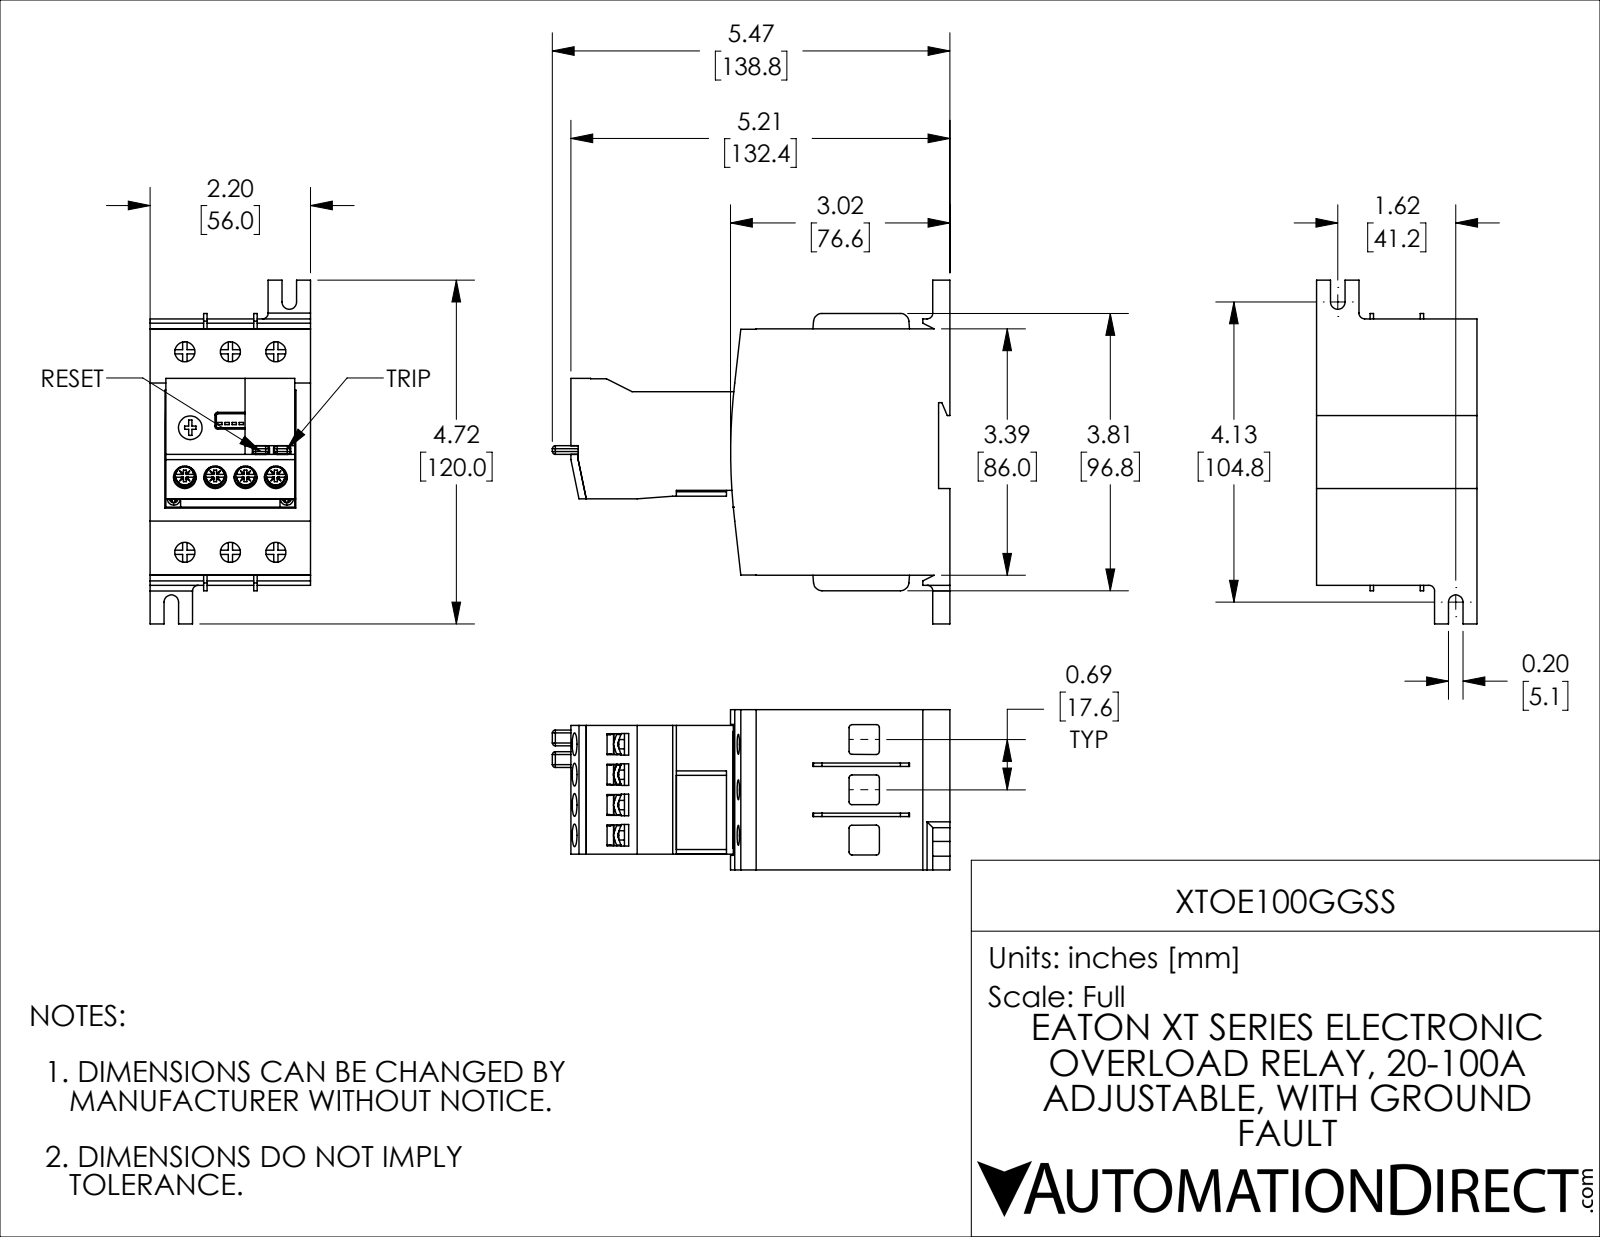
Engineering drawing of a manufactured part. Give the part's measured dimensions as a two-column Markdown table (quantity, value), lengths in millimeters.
| quantity | value |
| --- | --- |
| part name | XTOE100GGSS |
| STEP written by | SolidWorks 2018 (AUTOMOTIVE_DESIGN) |
| units | millimeters |
| bodies | 31 solids, 1045 faces (690 planar, 189 cylindrical, 166 other) |
| overall size | 138.9 × 120 × 56 |
| volume | 447 700 mm³ |
| surface area | 60 500 mm² |
| round holes (diameter × count) | 7 × 6, 3.6 × 4, 6.8 × 4, 8 × 4, 2.2 × 2, 3.2 × 2 |
| round bosses / shafts (diameter × count) | 3.4 × 4, 3.3 × 4, 2.8 × 4, 2.5 × 4, 4.5 × 2, 8.3 × 1, 4.6 × 1 |
| partial cylindrical surfaces (radius × count) | 0.5 × 24, 1 × 14, 2 × 12, 3 × 6, 0.4 × 2, 1.6 × 2, 2.5 × 2, 0.8 × 1 |
| main face-to-face distances | 56, 5.5, 50.5, 69.7, 86, 45, 64.1, 21.9, 34.5, 4 |
| hole center spacings | 10.6, 21.2, 26.7, 27.2, 43.3, 43.6, 71.8, 8.9 |
